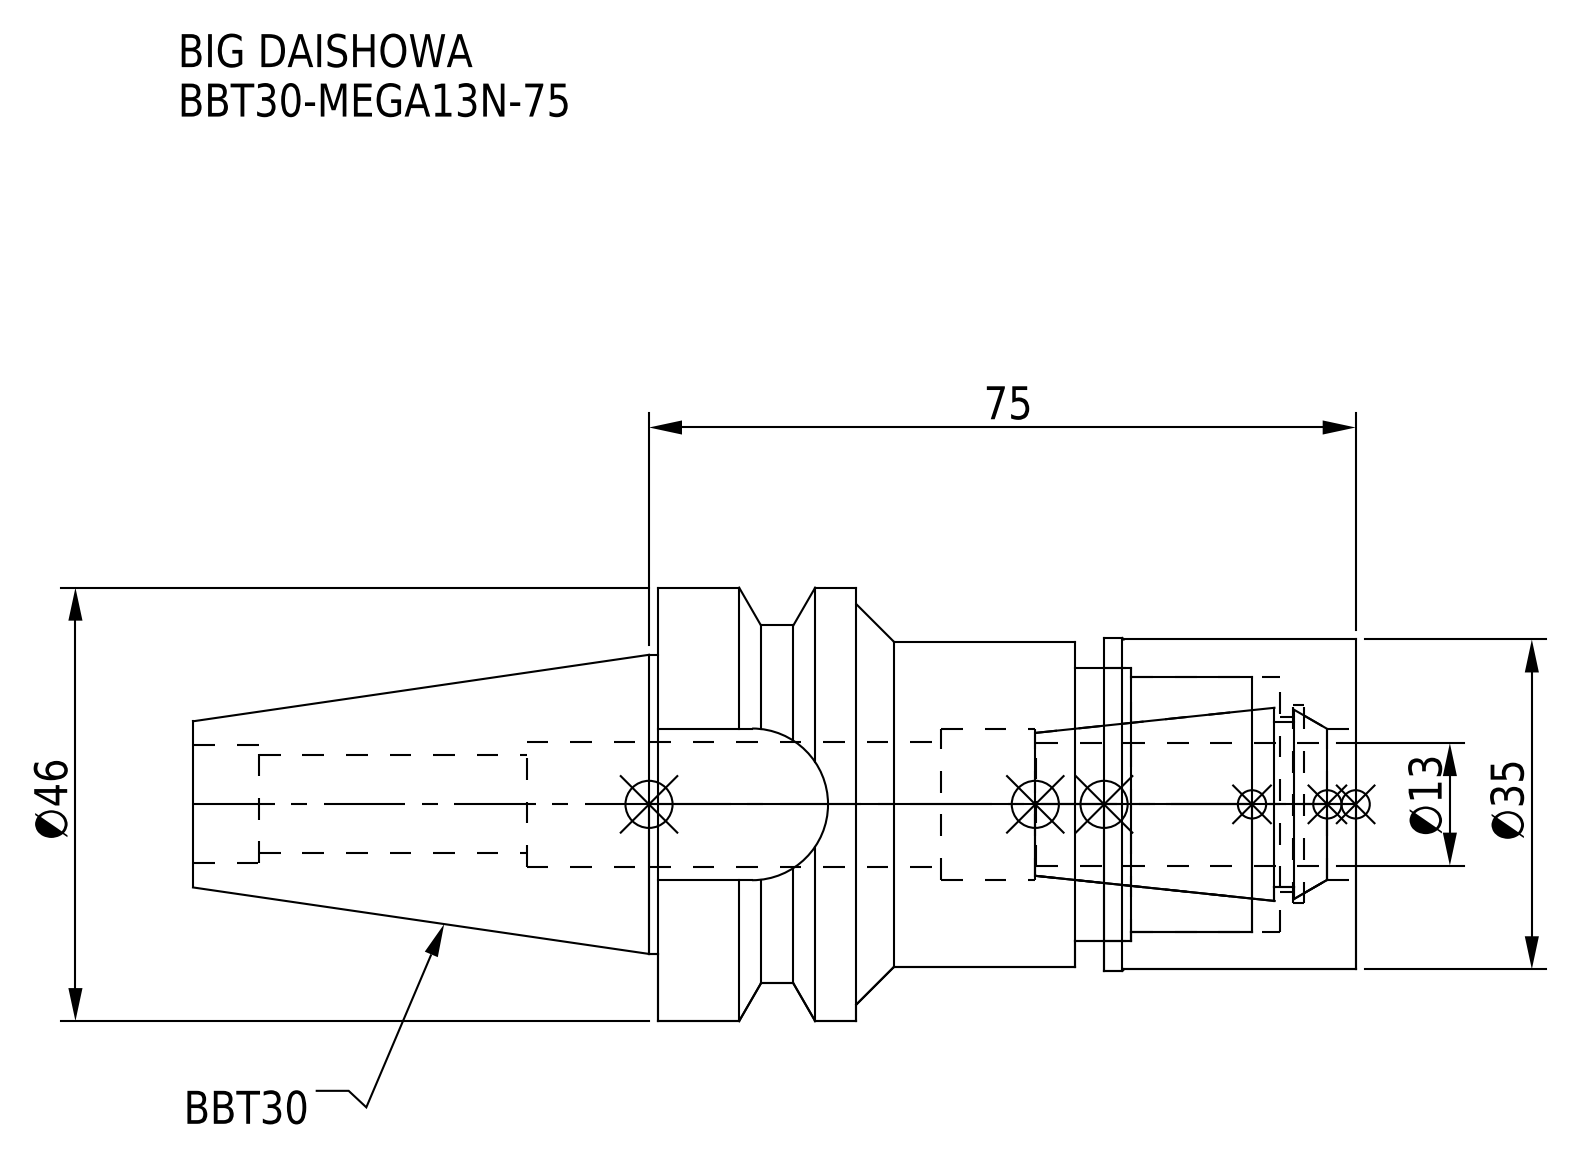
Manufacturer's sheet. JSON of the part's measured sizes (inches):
{"part_name": "MGN13_1.stp; DXF_TEMP_ASSY_ASM_4_ASM.stp; BBT30-MEGA13N-75-130.stp; BBT30-MEGA13N-75_1.stp (+3 more)", "step_written_by": "SolidWorks 2019 (CONFIG_CONTROL_DESIGN)", "units": "inches", "bodies": {"solids": 2, "faces": 76, "planar": 22, "cylindrical": 40, "other": 14}, "overall_size": [4.858, 1.811, 1.811], "volume_in3": 5.097, "surface_area_in2": 39.26, "round_holes": [[0.409, 1], [0.492, 1], [0.524, 1], [0.63, 1], [0.728, 1], [0.827, 1], [1.063, 1], [1.142, 1]], "round_bosses_or_shafts": [[1.811, 1], [1.39, 1], [1.378, 1], [1.358, 1], [1.25, 1]], "partial_cylinders_radius": [[0.317, 1], [0.748, 1]], "face_to_face_distances": [2.913, 1.051, 1.862, 0.315, 0.736, 2.598, 1.173, 0.858, 0.122, 1.74]}
